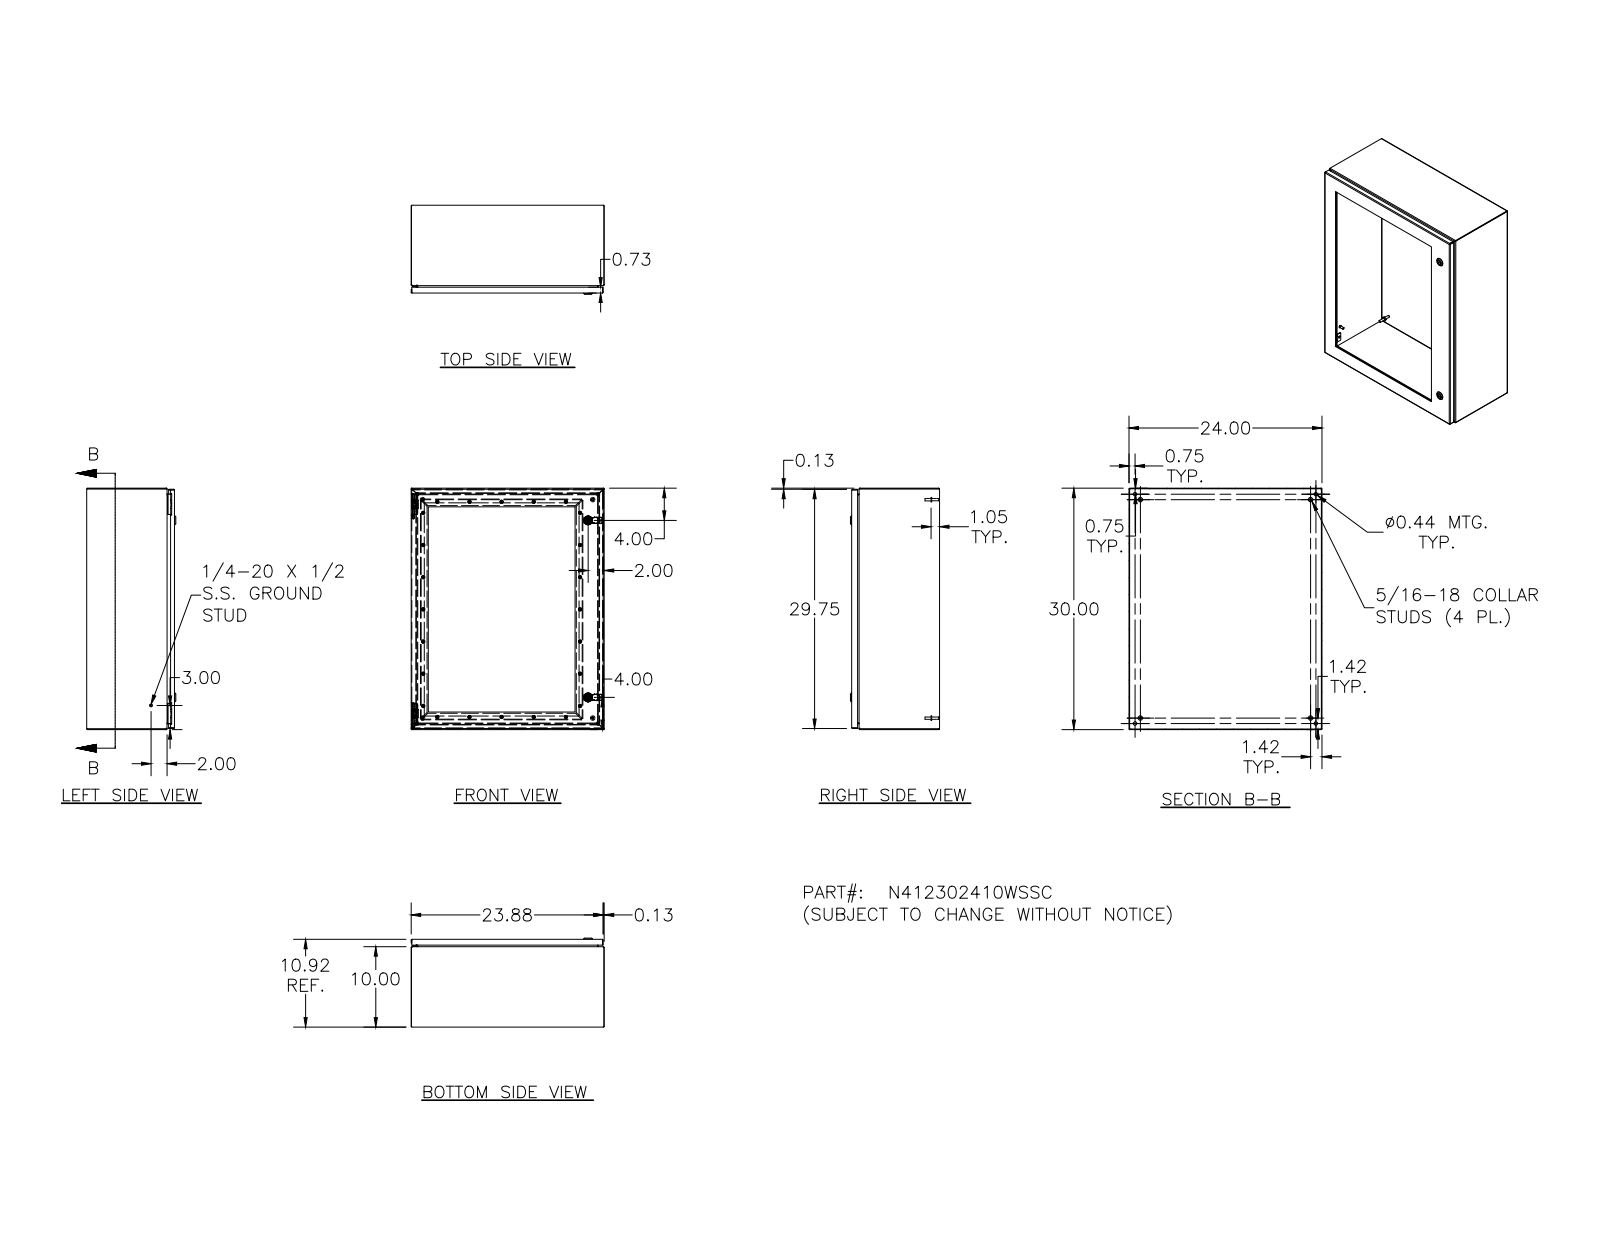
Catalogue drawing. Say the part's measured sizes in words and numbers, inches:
The part is named "N412302410WSSC; N412302410WSSCBKP; N4123024WSSCLID; HFW328176 (+8 more)". Its 3-D file was written by "Autodesk Inventor 2011 (AUTOMOTIVE_DESIGN)". It is 94 solids with 2494 faces: 1017 planar, 688 cylindrical and 789 other. Overall it measures 30 by 24 by 11.075 inches. Its volume is 303.7 cubic inches and its surface area 5 848 square inches. Round holes: 26 of diameter 0.156, 24 of diameter 0.281, 4 of diameter 0.093, 4 of diameter 0.152, 4 of diameter 0.167, 4 of diameter 0.172, 4 of diameter 0.188, 4 of diameter 0.437, 2 of diameter 0.197, 2 of diameter 0.315, 2 of diameter 0.394, 2 of diameter 0.402. Round bosses or shafts: 24 of diameter 0.19, 23 of diameter 0.253, 10 of diameter 0.25, 4 of diameter 0.563, 4 of diameter 0.36, 4 of diameter 0.32, 4 of diameter 0.3, 4 of diameter 0.275. Partial cylindrical surfaces (rounded edges, fillets, slot ends): 34 of radius 0.031, 26 of radius 0.05, 24 of radius 0.105, 18 of radius 0.016, 16 of radius 0.125, 15 of radius 0.02, 8 of radius 0.032, 8 of radius 0.157. The main face-to-face distances are 0.074, 10.843, 10.769, 23.926, 0.25, 10.593, 10.519, 29.926, 23.852, 24. The hole center spacings are 4, 8, 12, 27.047, 26, 27.92, 16, 26.75.
